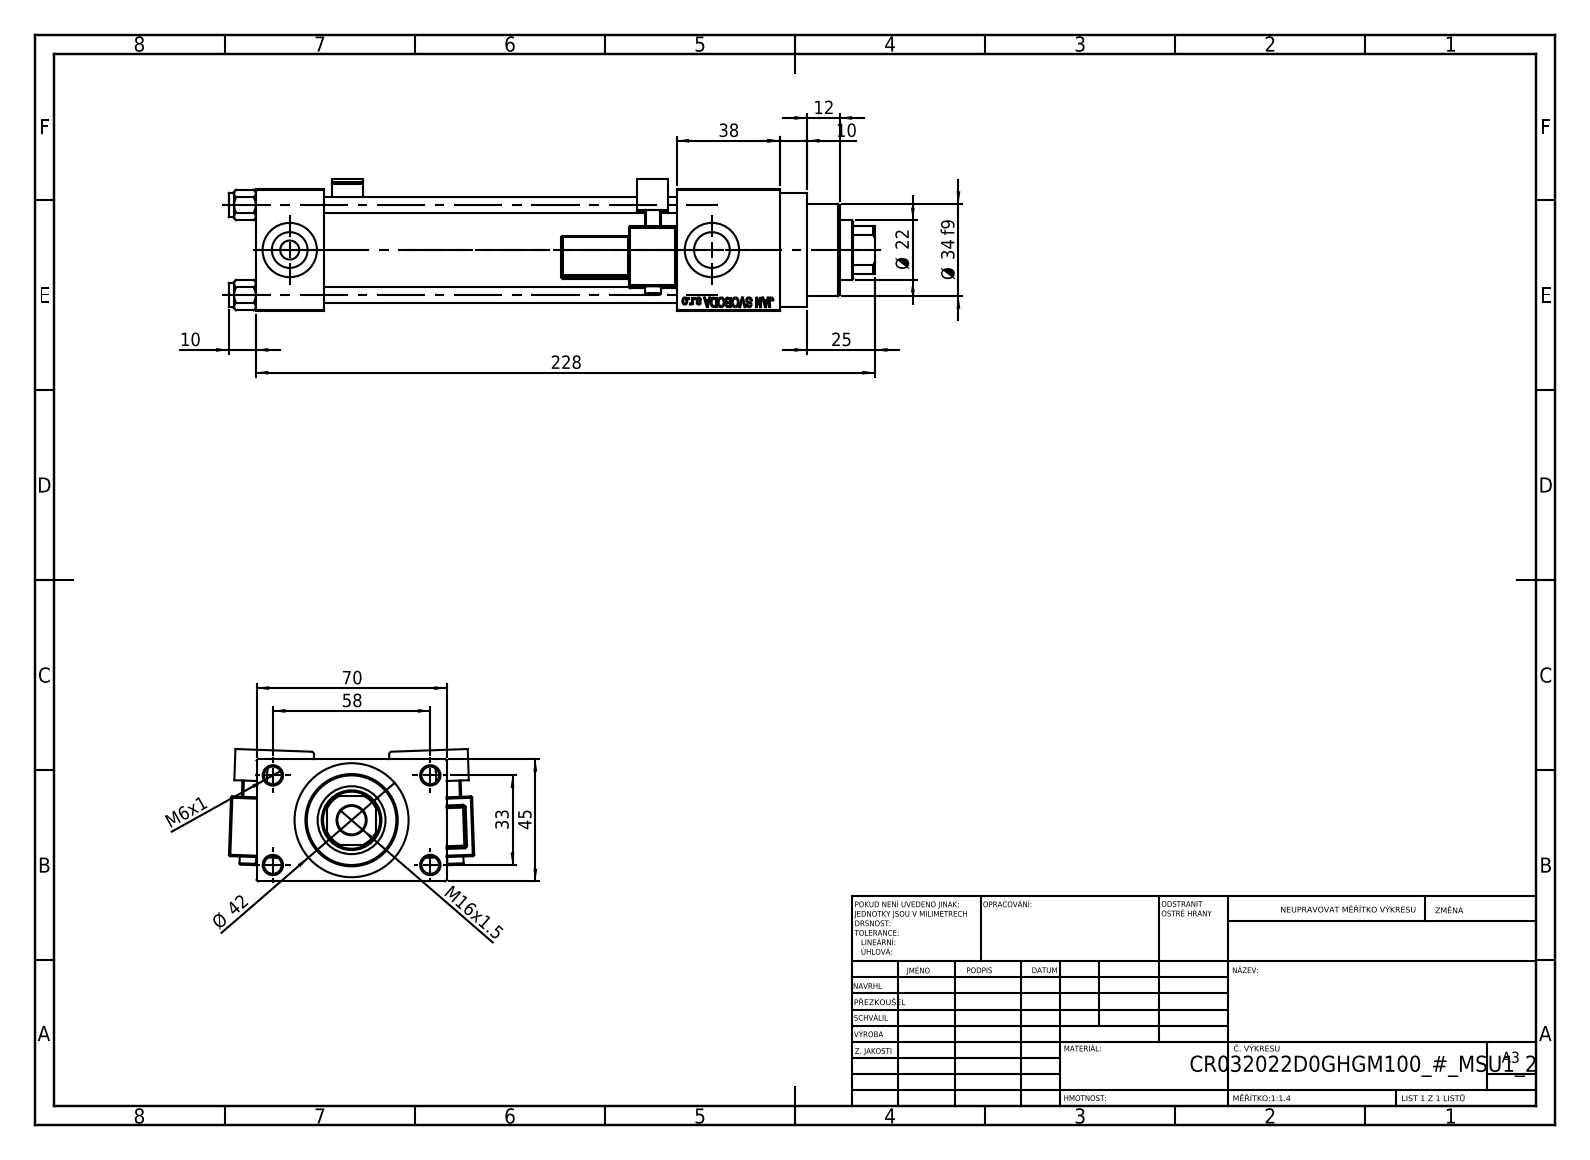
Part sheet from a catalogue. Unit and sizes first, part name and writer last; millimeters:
Units: millimetres
Overall size (bounding box): 238 × 90.31 × 48.72
Round holes (diameter × count): ⌀6 ×4, ⌀6.5 ×4, ⌀7 ×2, ⌀13.16 ×2, ⌀20 ×2, ⌀10.5 ×1, ⌀22 ×1, ⌀24 ×1, ⌀25 ×1, ⌀32 ×1, ⌀33 ×1
Round bosses / shafts (diameter × count): ⌀9 ×4, ⌀6 ×2, ⌀42 ×1, ⌀38 ×1, ⌀34 ×1
Partial cylindrical surfaces — rounded edges, fillets, slot ends (radius × count): R0.5 ×48, R1 ×2, R2.5 ×2, R4 ×2, R10.5 ×1
Main face-to-face distances: 45, 25, 130, 12.5, 3, 57.5, 155, 168, 38, 70
Hole centre spacings: 12.4, 23.48, 33.2, 33.37, 35.35, 45.6, 56.35, 33
Volume: 349 502 mm³ · Surface area: 121 126 mm²
Bodies: 13 solids, 1260 faces (558 planar, 148 cylindrical, 554 other)
Part name (STEP PRODUCT): NUT_M5_D; V215_VC_A; V215CR_D_Body; V215CR_MSU (+2 more)
STEP written by: SolidWorks 2019 (CONFIG_CONTROL_DESIGN)
